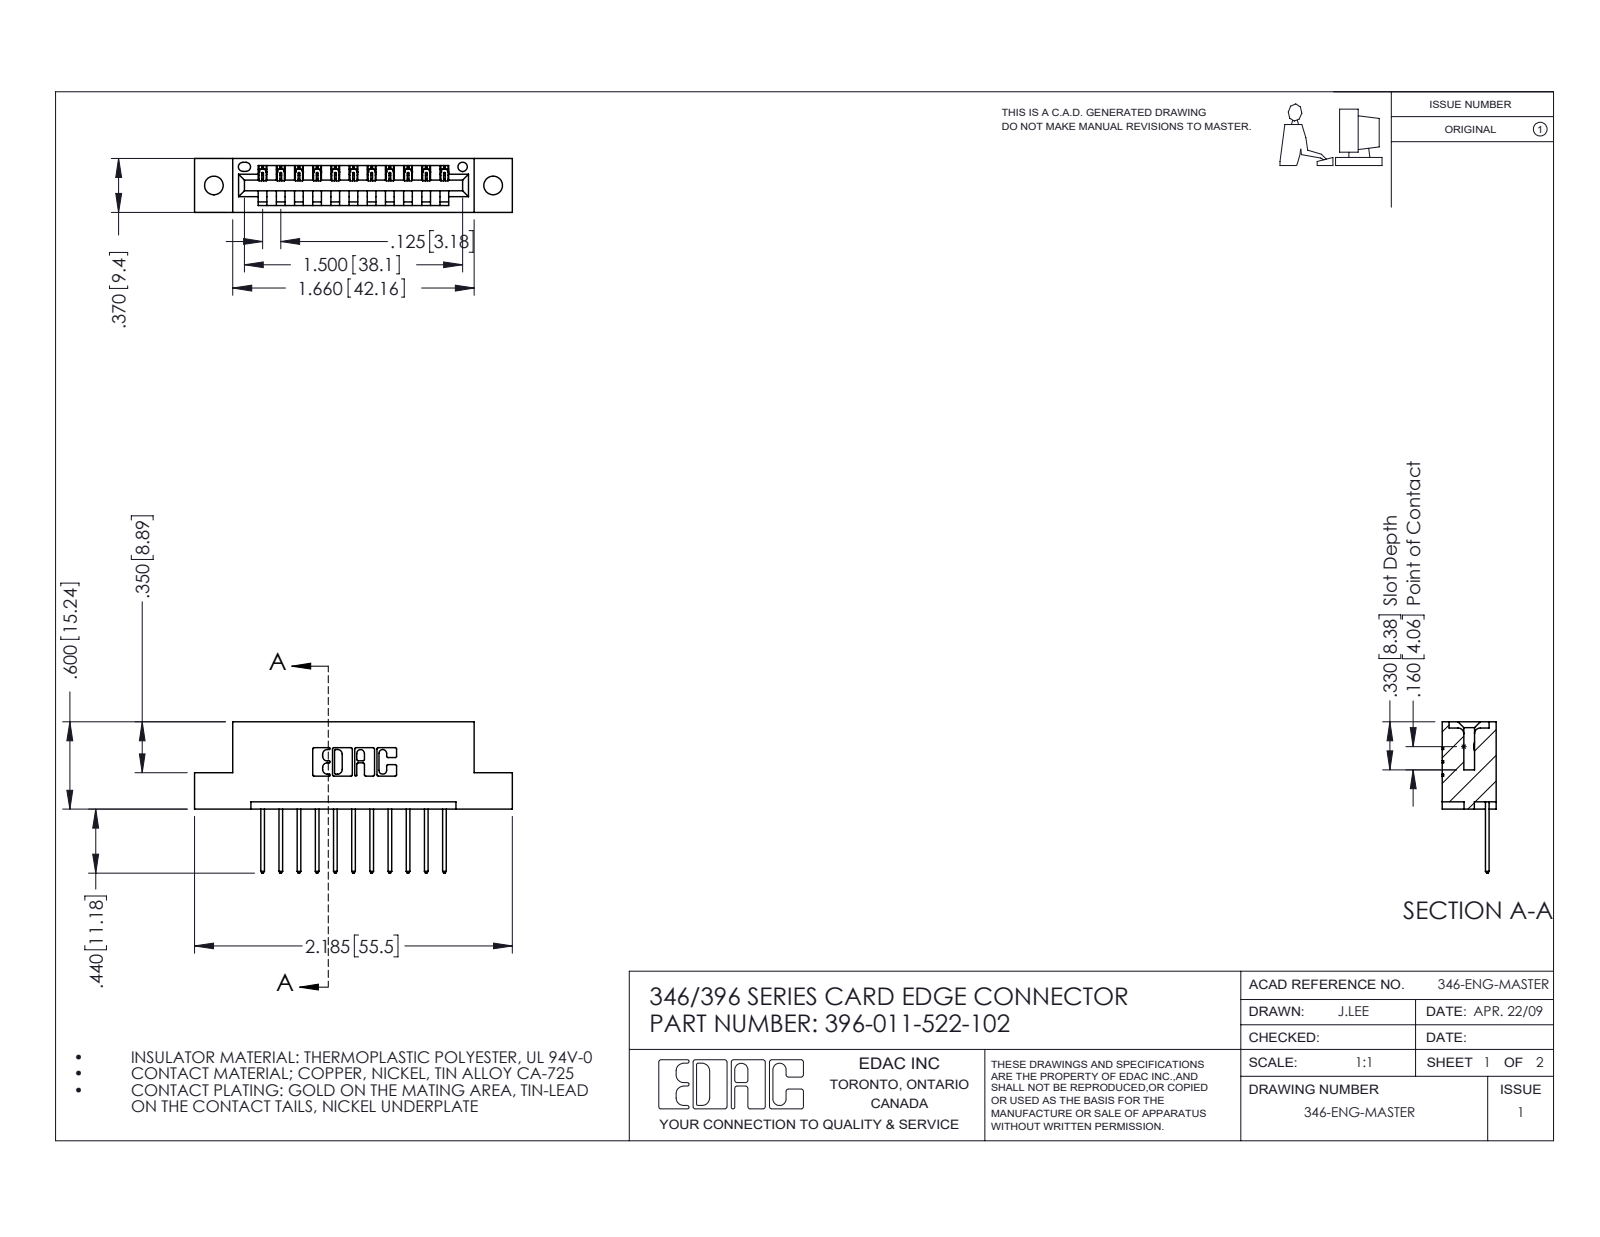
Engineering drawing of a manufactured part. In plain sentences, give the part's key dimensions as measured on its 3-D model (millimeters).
The part is named "345-292-001_345-293-122; 346 Part_Flush Mounting Lugs - 0.128 Dia; 396-011-522-102". Its 3-D file was written by "SolidWorks 2016 (CONFIG_CONTROL_DESIGN)". It is 12 solids with 760 faces: 516 planar, 244 cylindrical and 0 other. Overall it measures 55.5 by 26.4 by 9.4 millimeters. Its volume is 5 060 cubic millimeters and its surface area 5 764 square millimeters. Round holes: 2 of diameter 3.3, 1 of diameter 1.6. Partial cylindrical surfaces (rounded edges, fillets, slot ends): 22 of radius 0.2, 22 of radius 0.3, 22 of radius 0.3, 6 of radius 0.2, 6 of radius 0.8, 3 of radius 0.7, 2 of radius 0.8, 2 of radius 1. The main face-to-face distances are 6.4, 1.2, 8.2, 9.4, 1.8, 7.6, 0.6, 3.8, 5.6, 2.5. The hole center spacings are 6.2, 43.6, 48.8.
